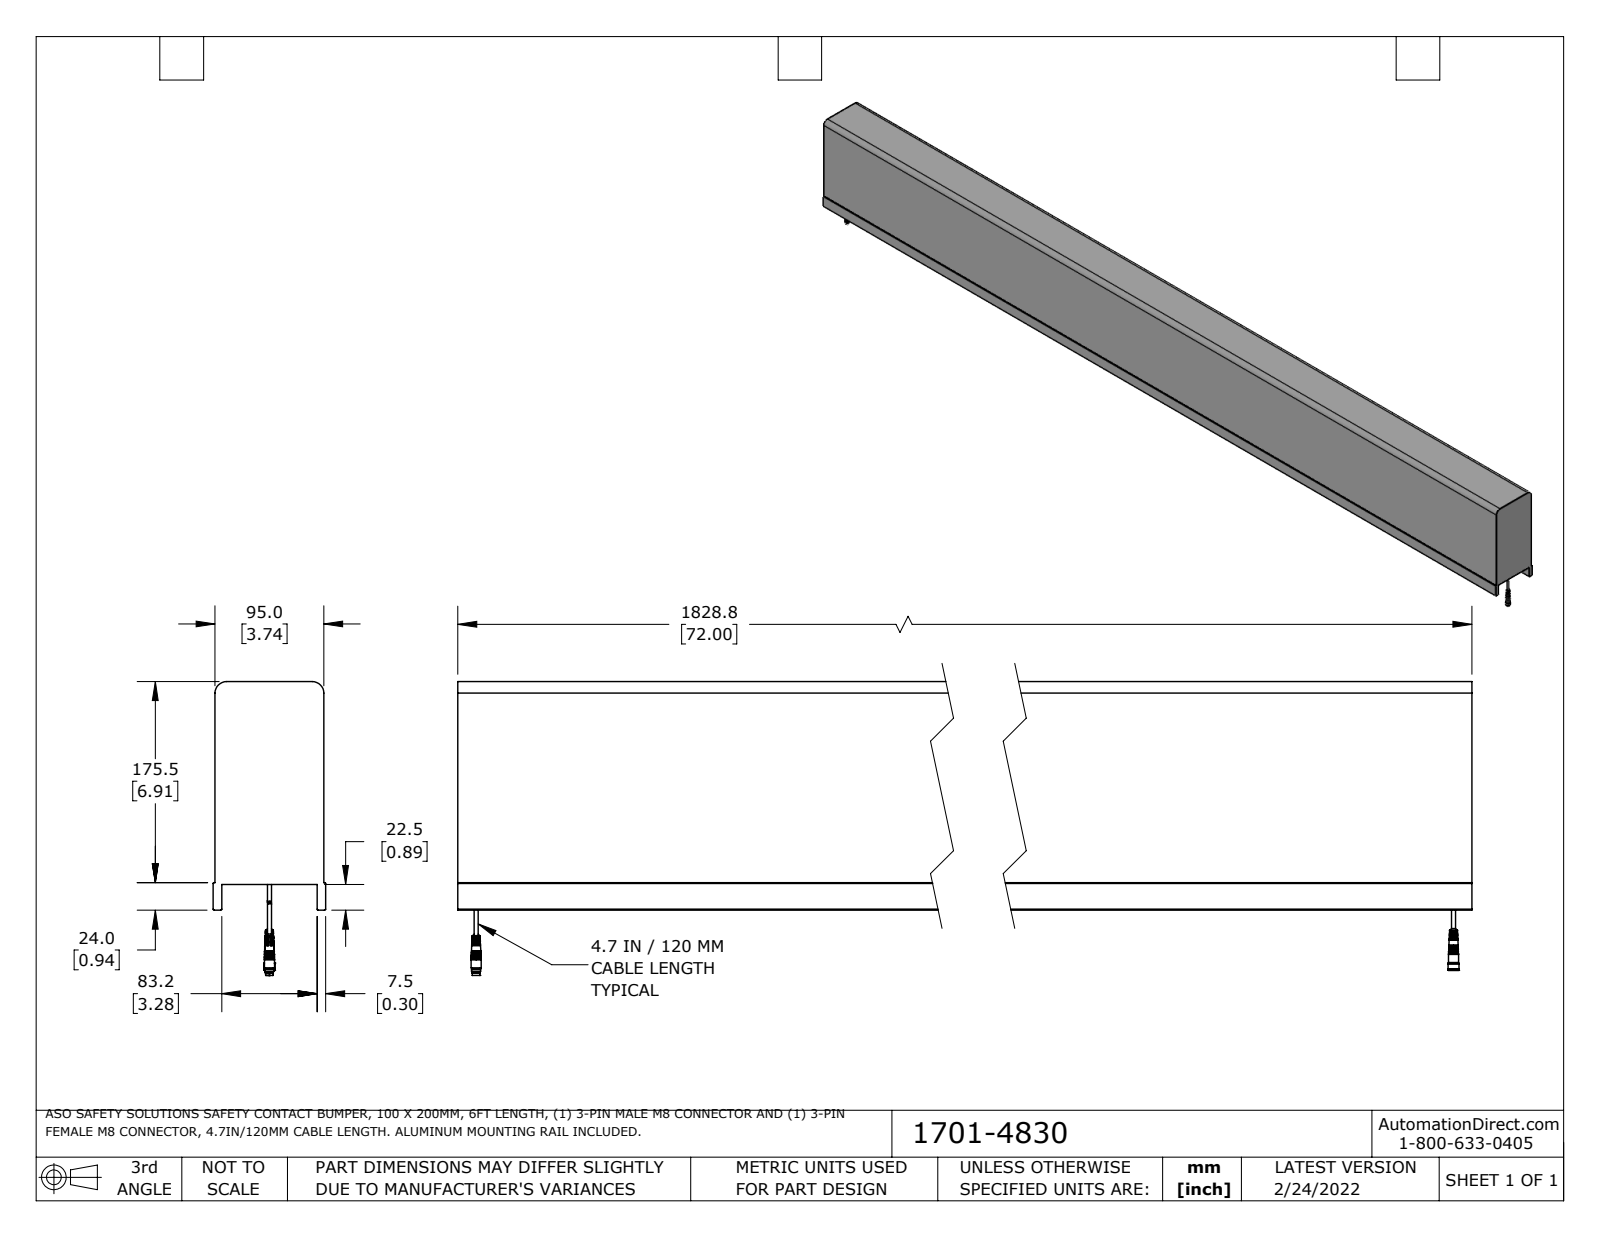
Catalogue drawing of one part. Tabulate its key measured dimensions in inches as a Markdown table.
| quantity | value |
| --- | --- |
| part name | 1701-4830_Default |
| STEP written by | SolidWorks 2021 (CONFIG_CONTROL_DESIGN) |
| units | inches |
| bodies | 24 solids, 447 faces (175 planar, 154 cylindrical, 118 other) |
| overall size | 72 × 10.096 × 3.868 |
| volume | 1 910 in³ |
| surface area | 1 848 in² |
| round holes (diameter × count) | 0.047 × 4, 0.033 × 3, 0.063 × 3, 0.134 × 2, 0.228 × 1, 0.232 × 1, 0.272 × 1, 0.283 × 1 |
| round bosses / shafts (diameter × count) | 0.047 × 8, 0.039 × 6, 0.02 × 4, 0.346 × 2, 0.224 × 2, 0.138 × 2, 0.378 × 1, 0.354 × 1 |
| partial cylindrical surfaces (radius × count) | 0.039 × 4, 0.03 × 2, 0.394 × 2 |
| main face-to-face distances | 3.74, 6.969, 0.064, 3.804, 0.295, 3.572, 0.231, 3.509, 3.868, 3.277 |
| hole center spacings | 70.74, 0.028, 0.069, 70.671, 70.713, 70.768, 70.809, 0.041 |
